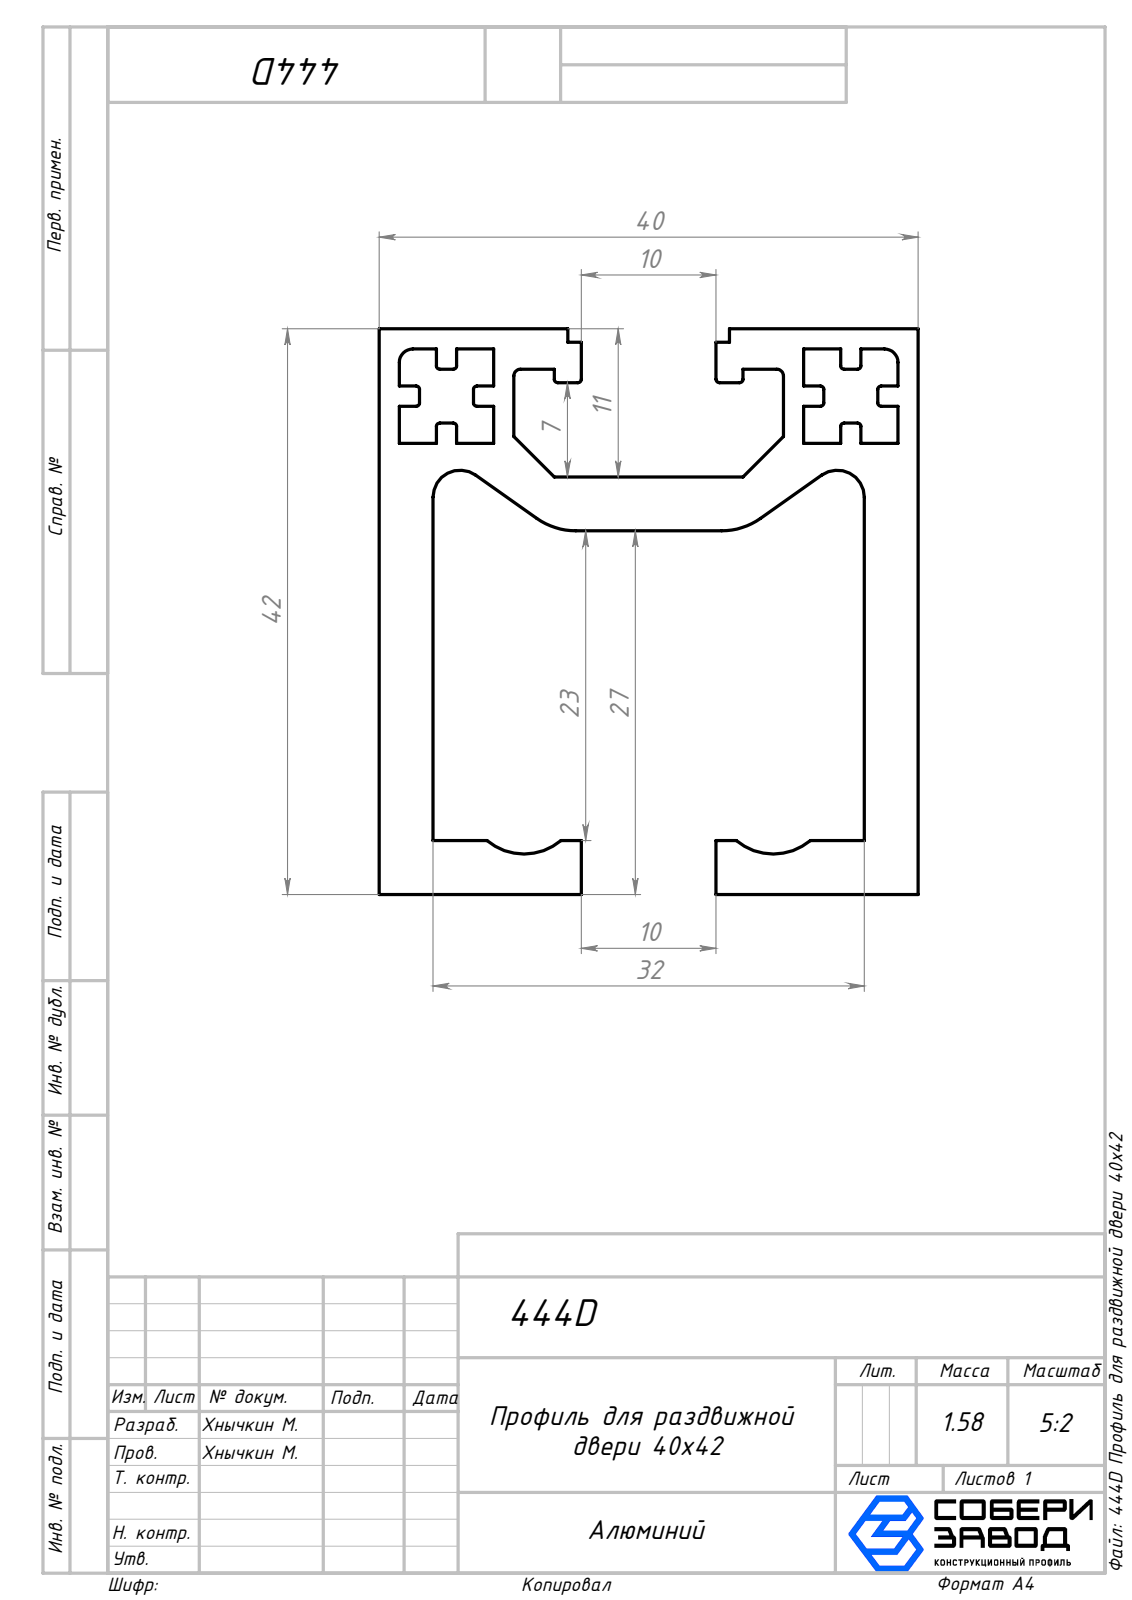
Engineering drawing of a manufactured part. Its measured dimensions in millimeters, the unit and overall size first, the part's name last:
Units: millimetres
Overall size (bounding box): 1000 × 42 × 40
Partial cylindrical surfaces — rounded edges, fillets, slot ends (radius × count): R0.25 ×20, R0.5 ×2, R1 ×2, R2 ×2, R4.28 ×2, R5 ×2
Main face-to-face distances: 4, 36, 1.5, 40, 4.25, 11, 15, 8.5, 2.75, 42
Volume: 586 677 mm³ · Surface area: 393 031 mm²
Bodies: 1 solid, 106 faces (76 planar, 30 cylindrical, 0 other)
Part name (STEP PRODUCT): 444D Профиль для раздвижной двери 40х42
STEP written by: SolidWorks 2026 (AUTOMOTIVE_DESIGN)
